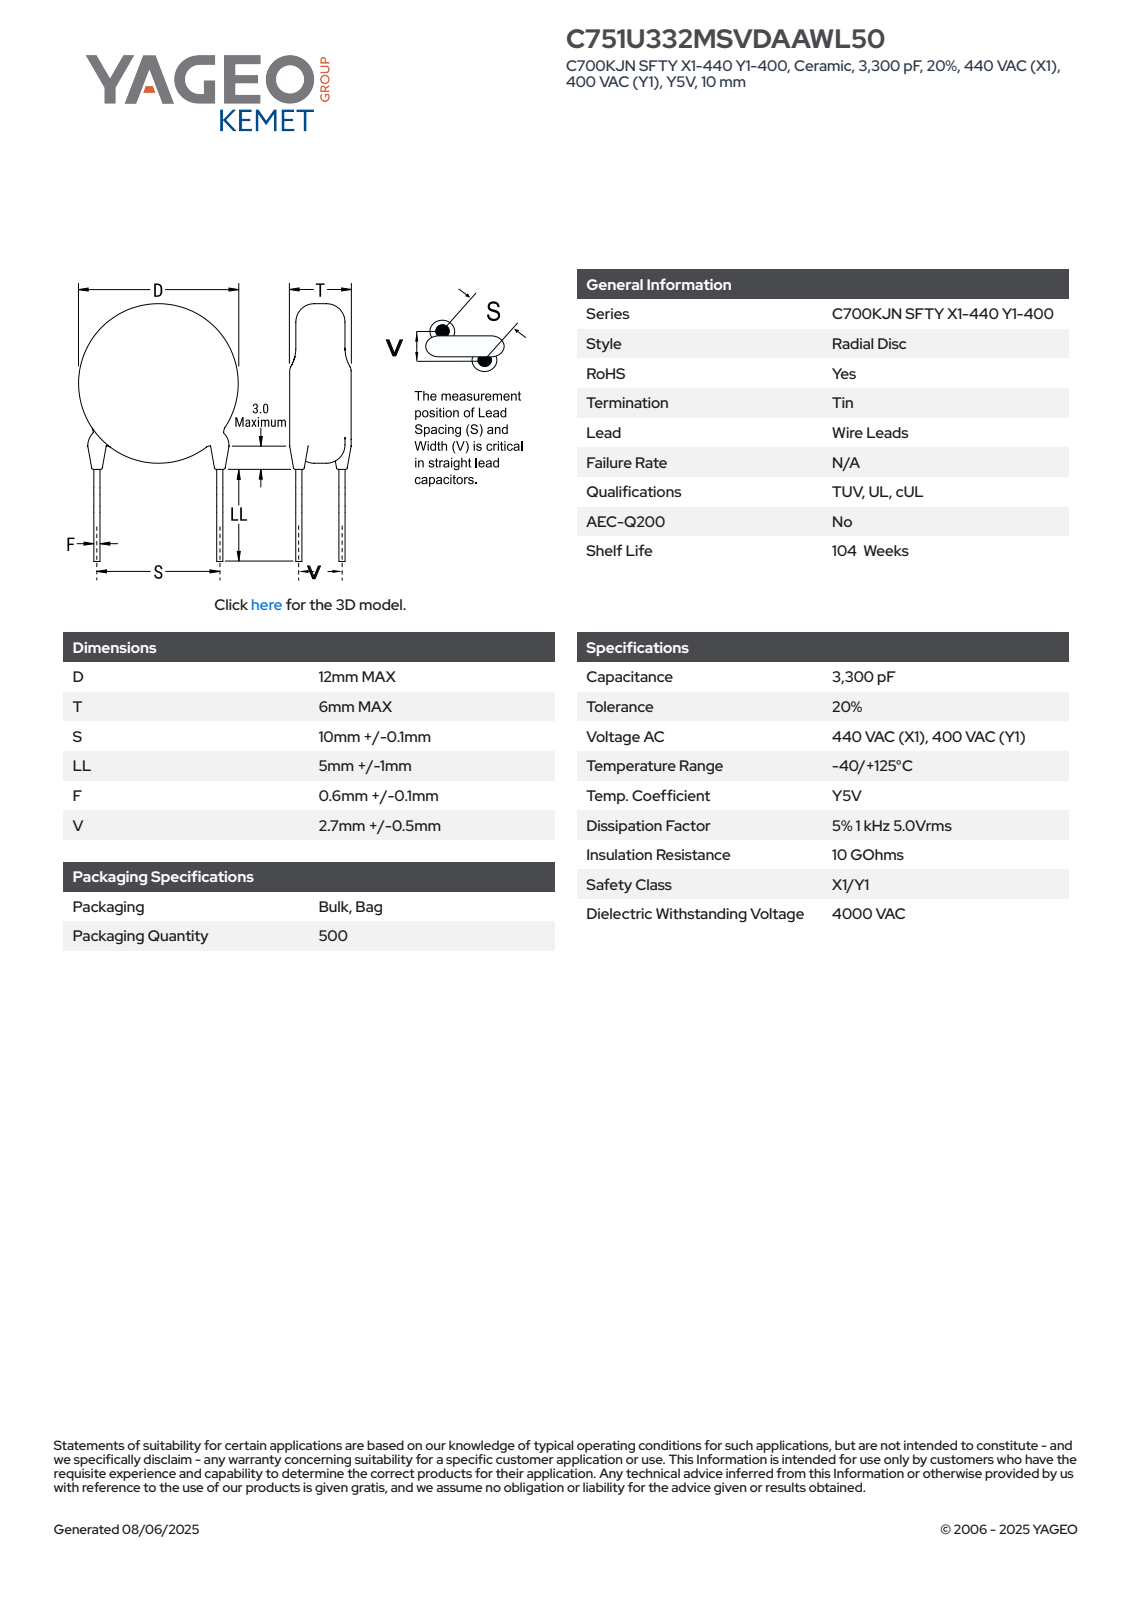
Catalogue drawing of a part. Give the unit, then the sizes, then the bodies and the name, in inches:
Units: inches
Overall size (bounding box): 0.738 × 0.472 × 0.236
Round bosses / shafts (diameter × count): ⌀0.047 ×4, ⌀0.028 ×2, ⌀0.472 ×1
Main face-to-face distances: 0.236, 0.538, 0.302, 0.484, 0.248, 0.054, 0.015, 0.043, 0.219, 0.159
Volume: 0.041 in³ · Surface area: 0.746 in²
Bodies: 4 solids, 80 faces (63 planar, 13 cylindrical, 4 other)
Part name (STEP PRODUCT): CCD_KST_12X6_D12T6S10.1LL6F0.7V2.7
STEP written by: SolidWorks 2021 (AUTOMOTIVE_DESIGN)
